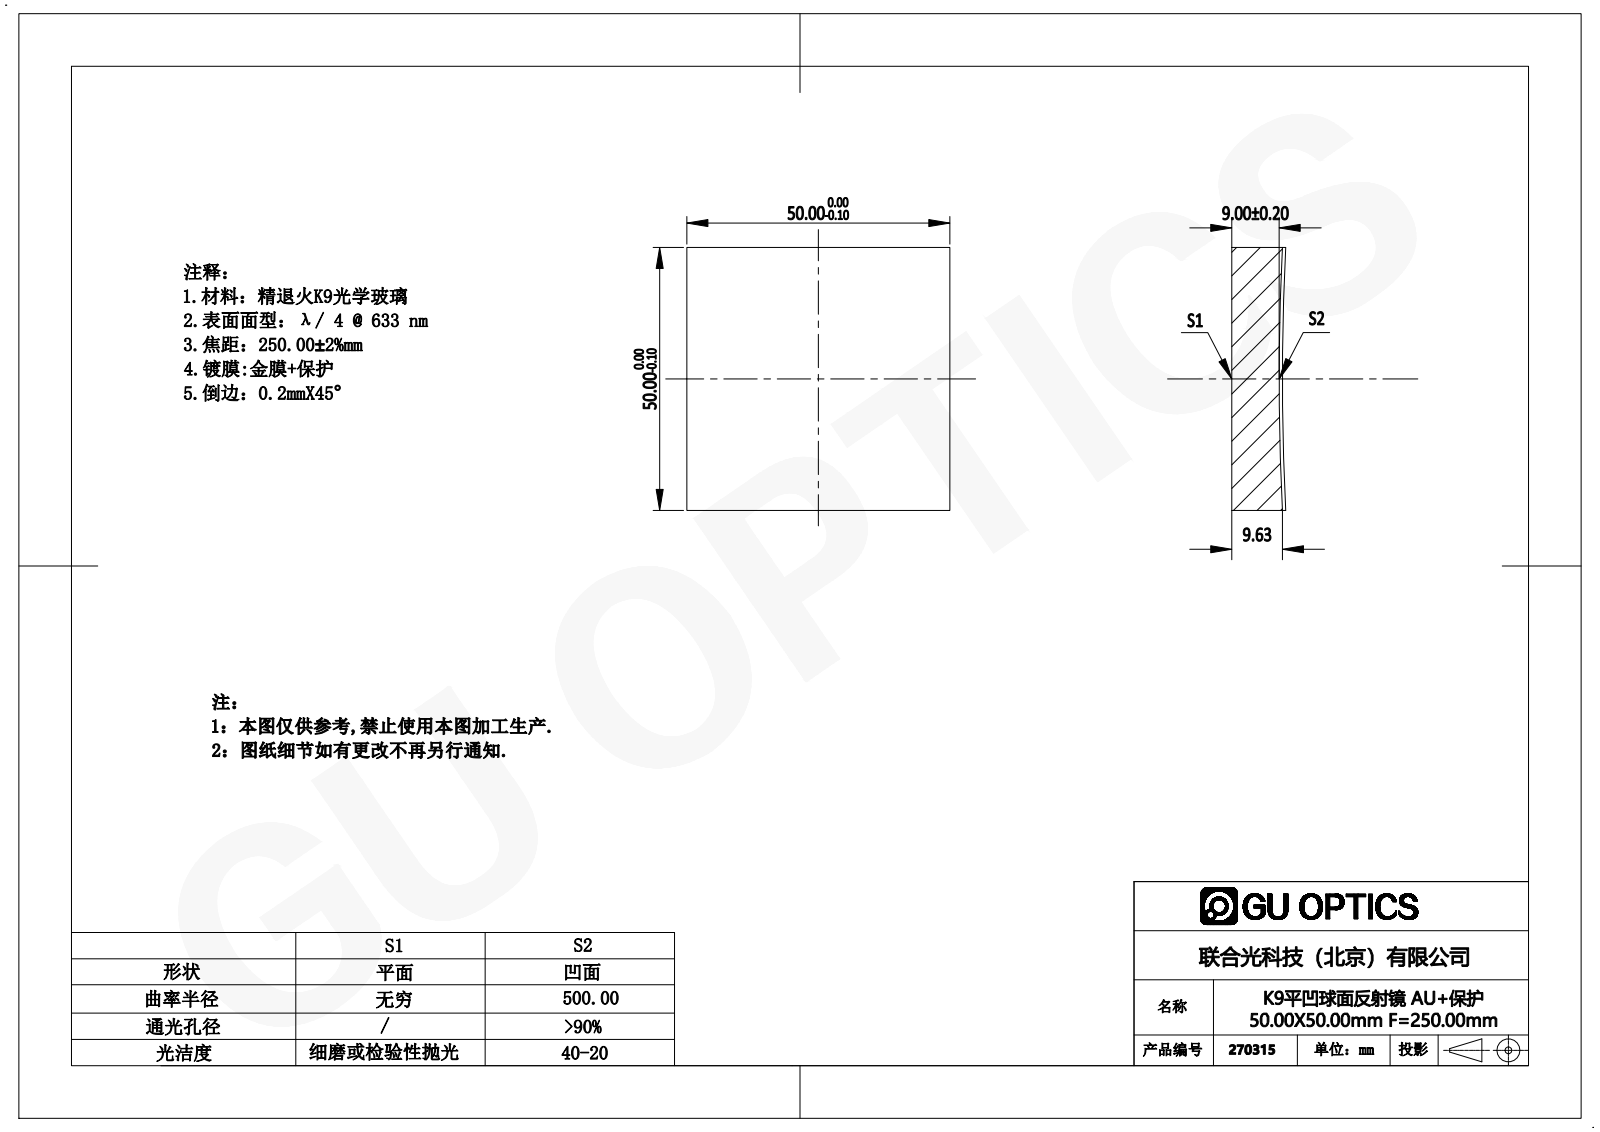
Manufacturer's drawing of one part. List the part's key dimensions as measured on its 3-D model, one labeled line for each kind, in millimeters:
Part name (STEP PRODUCT): 270055
STEP written by: SolidWorks 2019 (AUTOMOTIVE_DESIGN)
Units: millimetres
Bodies: 1 solid, 7 faces (5 planar, 0 cylindrical, 2 other)
Overall size (bounding box): 50 × 50 × 10.25
Volume: 23 542 mm³ · Surface area: 6 969 mm²
Main face-to-face distances: 50
